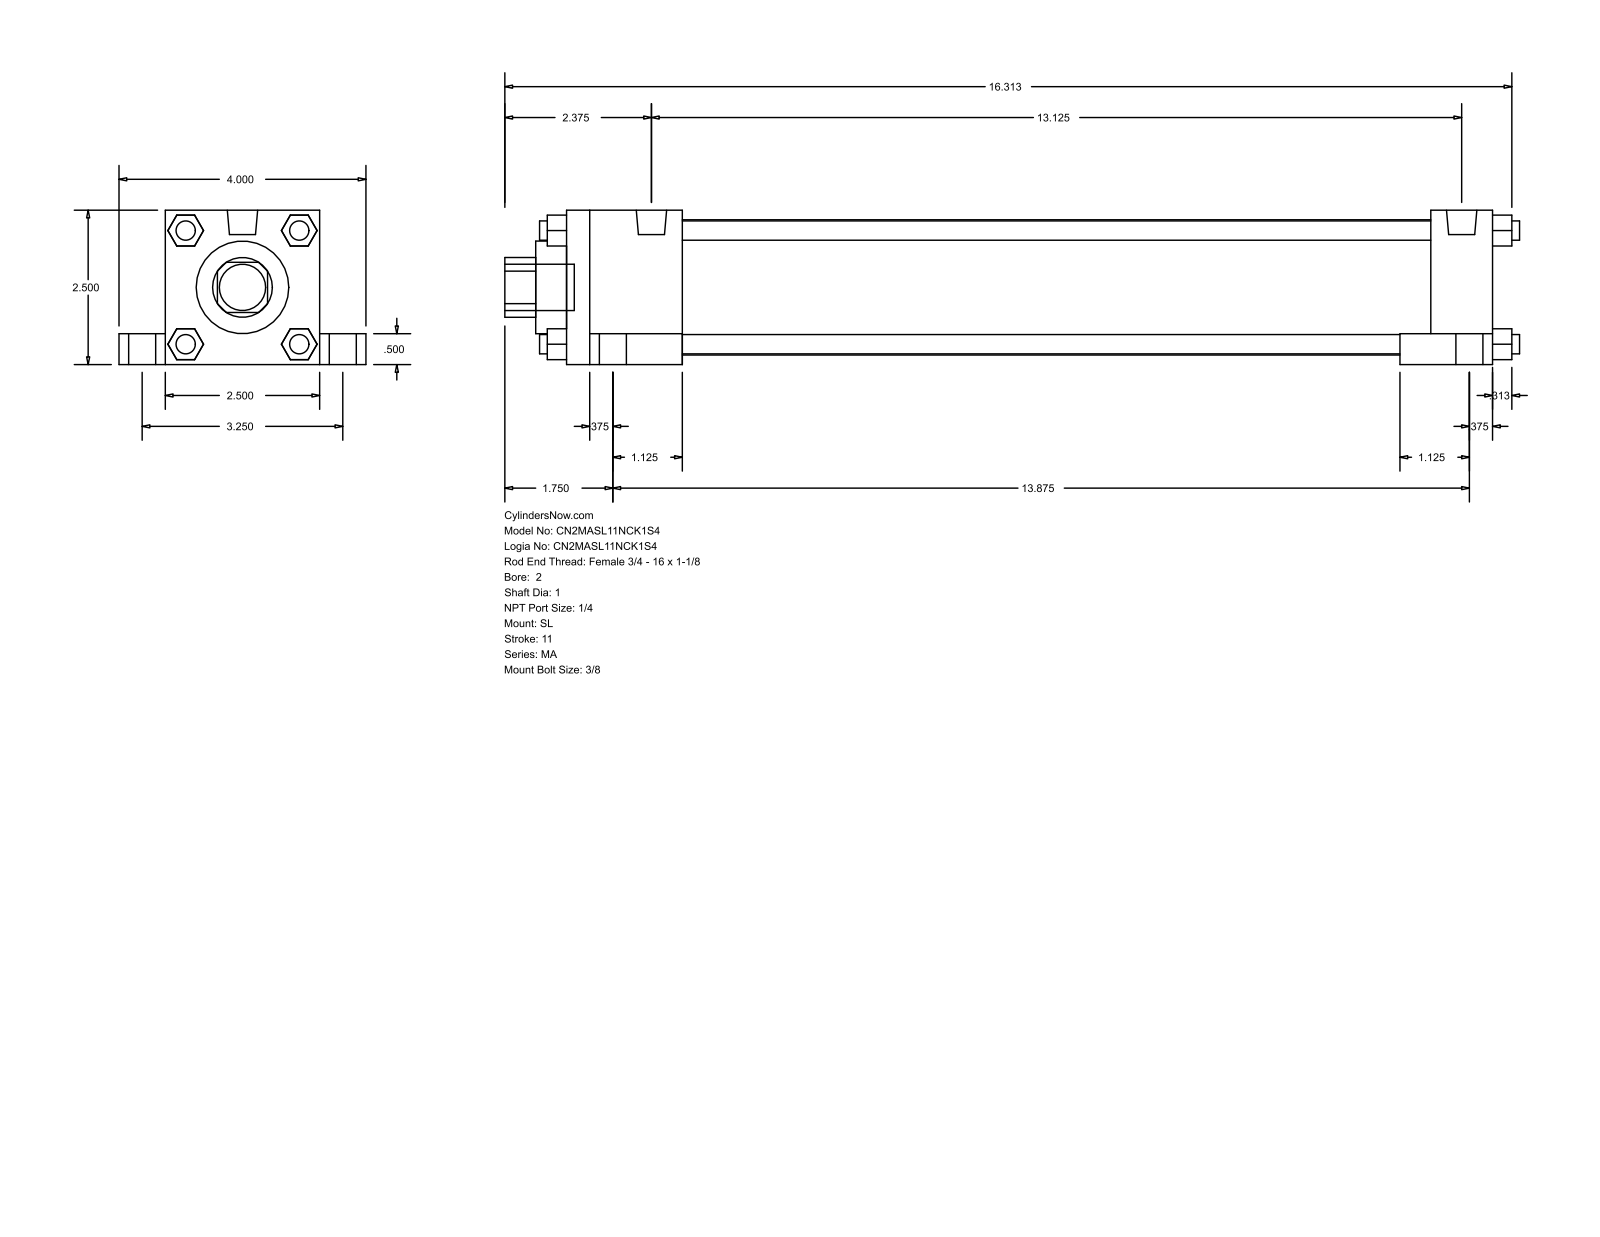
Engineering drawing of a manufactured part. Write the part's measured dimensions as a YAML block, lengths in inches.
part_name: "MA_SL__0200_1"
step_written_by: "GSSL Pune (CONFIG_CONTROL_DESIGN)"
units: inches
bodies: {solids: 0, faces: 148, planar: 112, cylindrical: 36, other: 0}
overall_size: [16.437, 4, 2.5]
round_holes:
  - {diameter: 1, count: 1}
  - {diameter: 1.5, count: 1}
  - {diameter: 2.19, count: 1}
round_bosses_or_shafts:
  - {diameter: 0.313, count: 8}
  - {diameter: 0.687, count: 4}
  - {diameter: 0.437, count: 4}
  - {diameter: 0.492, count: 2}
  - {diameter: 0.75, count: 1}
partial_cylinders:
  - {radius: 0.484, count: 1}
face_to_face_distances: [2.5, 0.5, 15, 0.75, 3.25, 1, 2, 1.875, 13.125, 14]
